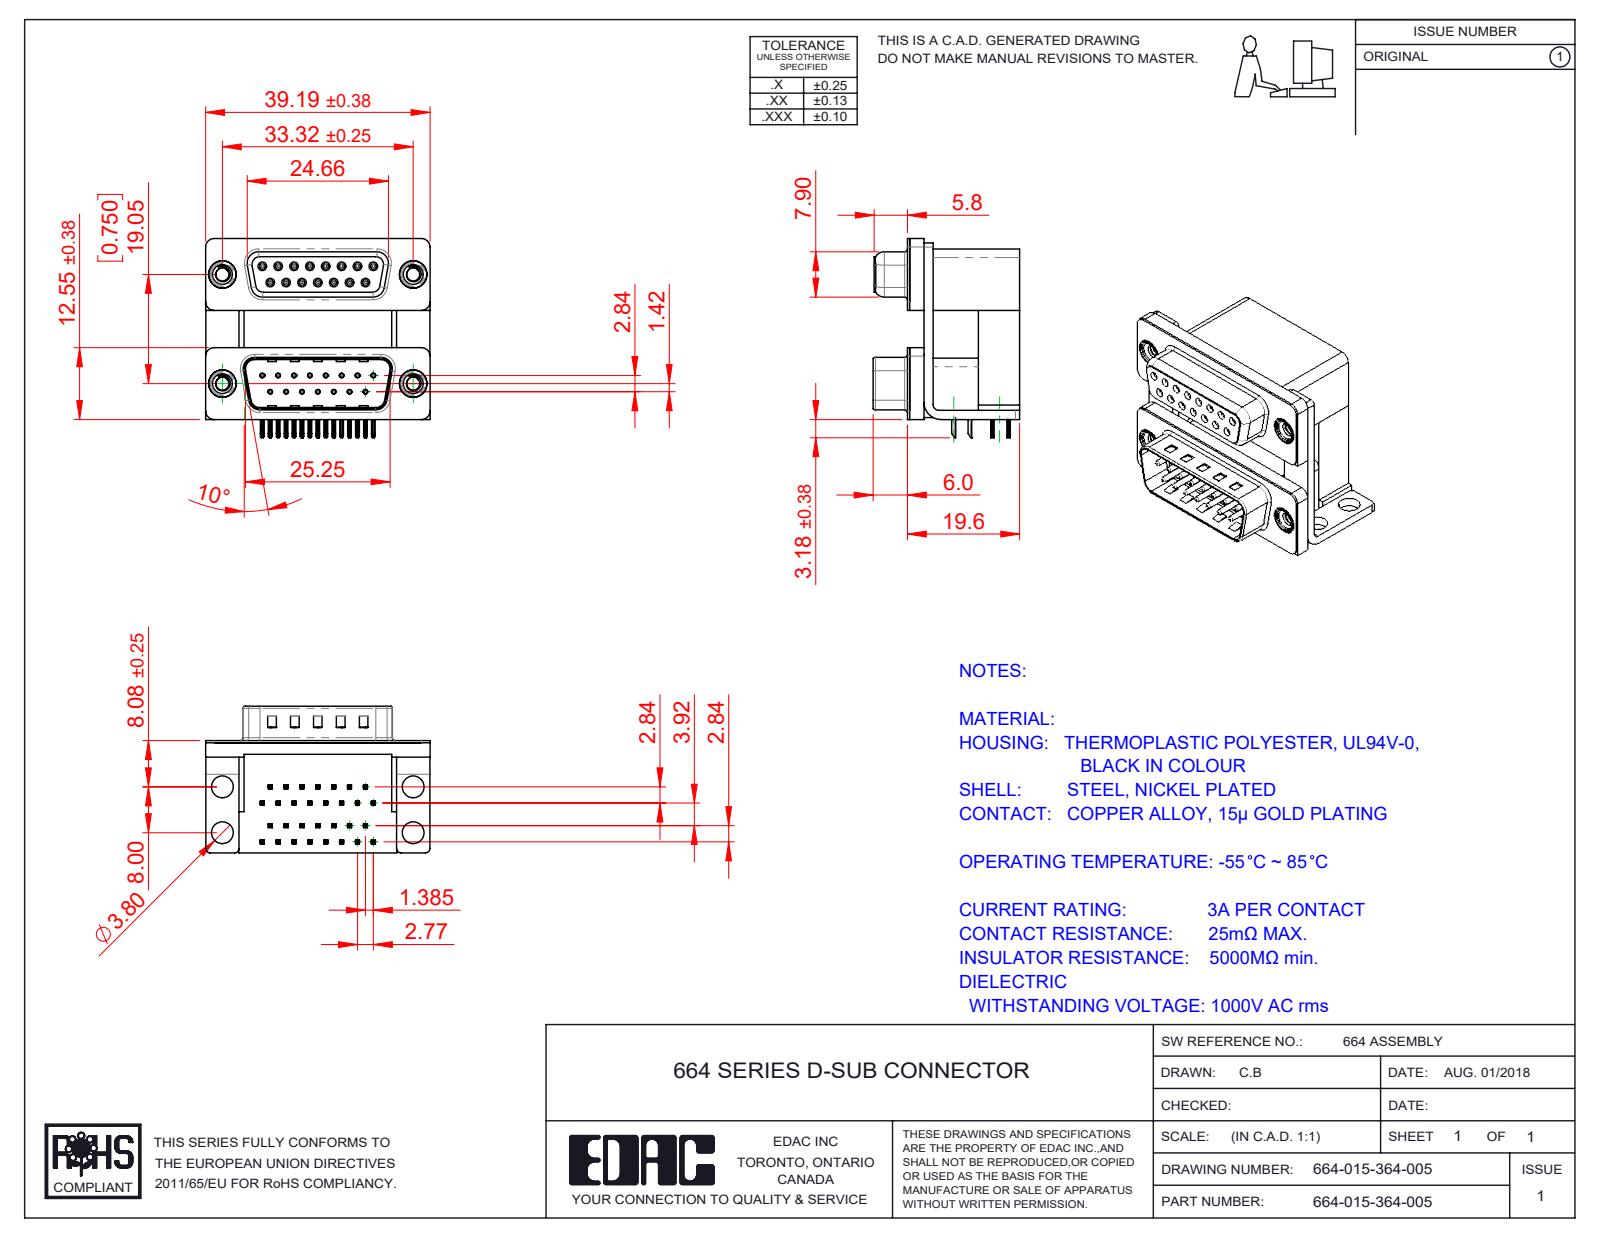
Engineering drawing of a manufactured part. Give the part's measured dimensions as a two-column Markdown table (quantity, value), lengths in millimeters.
| quantity | value |
| --- | --- |
| part name | 664 Contact Top Lower; 664 Contact Bottom Upper_M; 664 Housing Upper_15 Contacts M; 664 Shell Receptacle_15 Contacts (+8 more) |
| STEP written by | SolidWorks 2020 (CONFIG_CONTROL_DESIGN) |
| units | millimeters |
| bodies | 41 solids, 3912 faces (2015 planar, 1014 cylindrical, 883 other) |
| overall size | 39.19 × 34.78 × 25.6 |
| volume | 15 156 mm³ |
| surface area | 16 801 mm² |
| round holes (diameter × count) | 0.8 × 30, 0.35 × 15, 0.9 × 15, 2.26 × 4, 3.5 × 4, 3.8 × 4, 4 × 4, 4.8 × 4, 5 × 4 |
| round bosses / shafts (diameter × count) | 1.2 × 15, 0.75 × 15, 4.9 × 4, 4.75 × 4, 3.9 × 4 |
| partial cylindrical surfaces (radius × count) | 0.1 × 120, 0.15 × 60, 0.25 × 60, 0.12 × 30, 0.35 × 30, 1.5 × 16, 0.34 × 15, 0.5 × 12 |
| main face-to-face distances | 0.4, 19.2, 16.7, 2.5, 7.2, 12, 9.5, 10.69, 2.19, 2.9 |
| hole center spacings | 3.16, 2.77, 19.25, 5.54, 19.84, 8.31, 19.05, 20.78 |
